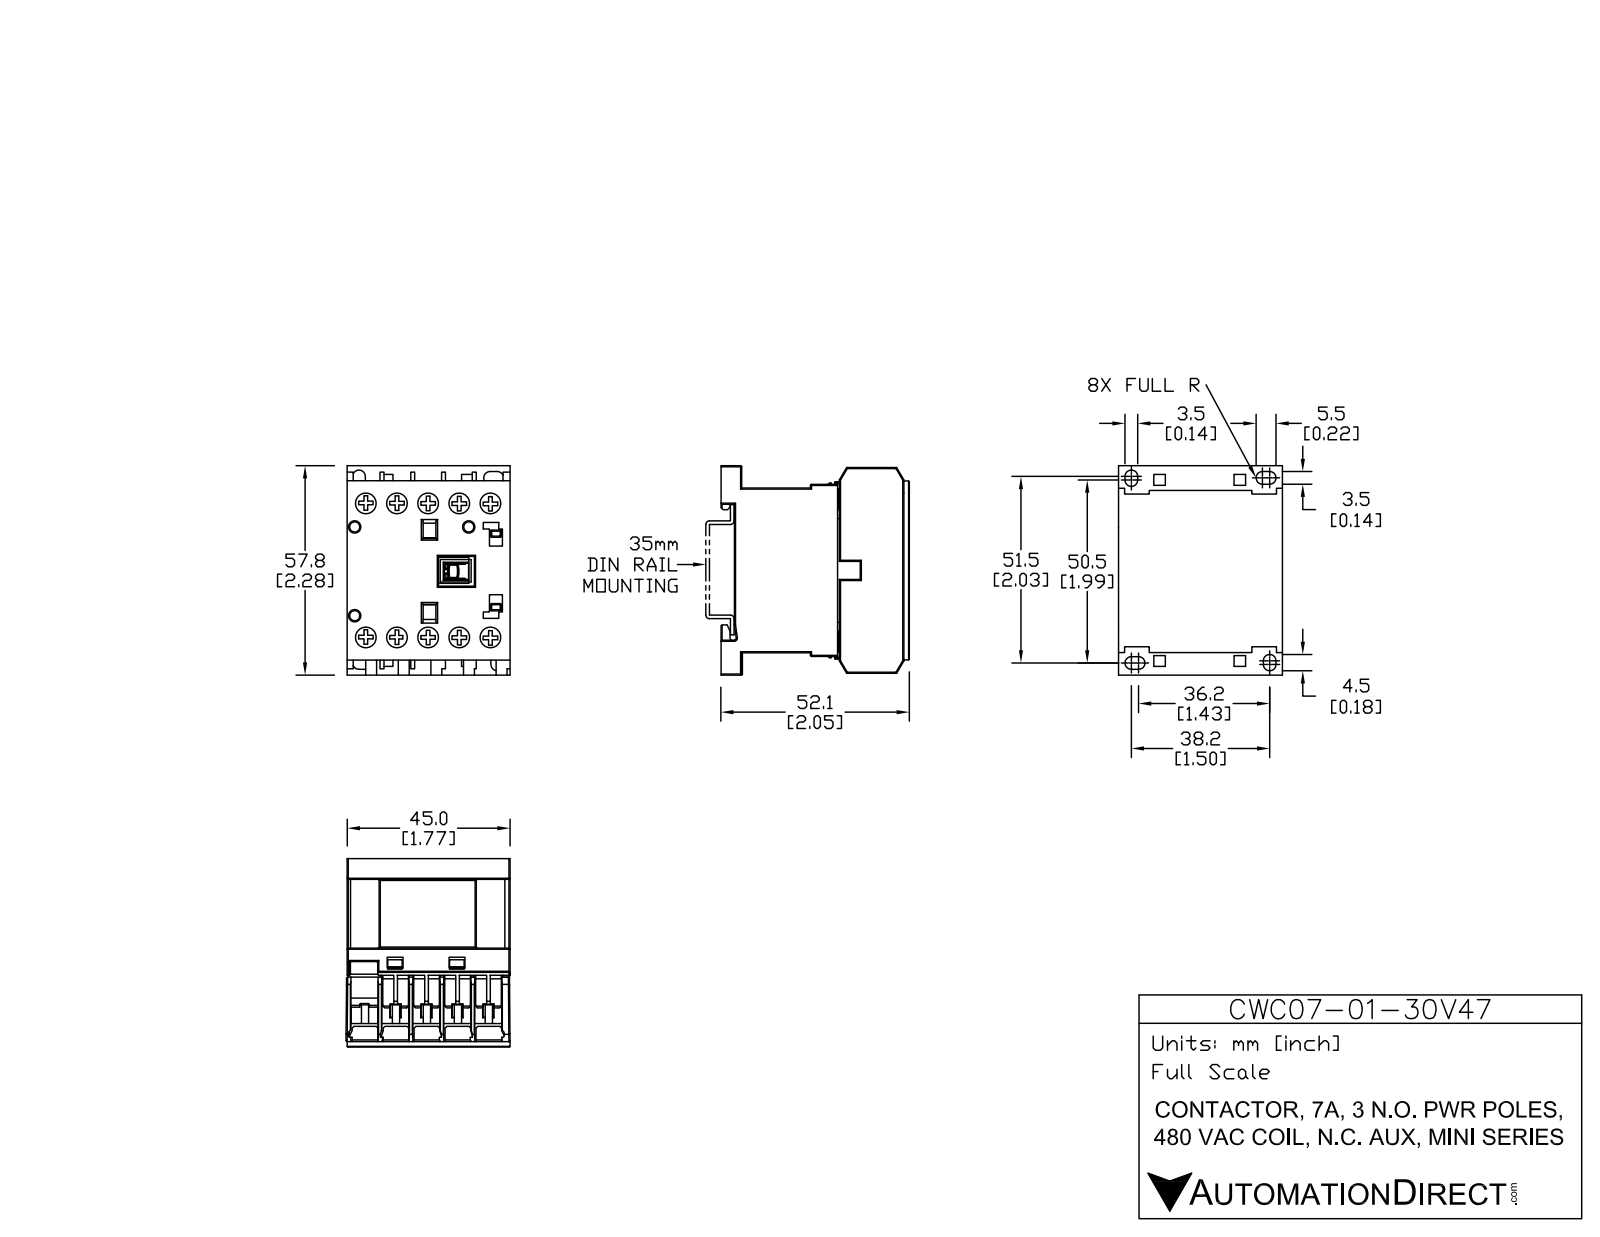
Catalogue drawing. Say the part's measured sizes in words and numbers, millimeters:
The part is named "CWC07-01-30V47". Its 3-D file was written by "SolidWorks 2013 (AUTOMOTIVE_DESIGN)". It is 15 solids with 535 faces: 445 planar, 90 cylindrical and 0 other. Overall it measures 58.04 by 52.12 by 45.75 millimeters. Its volume is 97 133 cubic millimeters and its surface area 30 437 square millimeters. Round holes: 10 of diameter 6.2, 3 of diameter 2.8. Round bosses or shafts: 10 of diameter 5.9. Partial cylindrical surfaces (rounded edges, fillets, slot ends): 20 of radius 0.3, 6 of radius 1.72, 2 of radius 1.73, 1 of radius 0.32, 1 of radius 0.42, 1 of radius 0.55. The main face-to-face distances are 8.25, 45.5, 1.25, 16.5, 9.5, 5.5, 17.75, 5.13, 10.63, 7. The hole center spacings are 8.55, 37.94, 17.1, 40.72, 36.96, 25.65, 44.99, 6.91.
